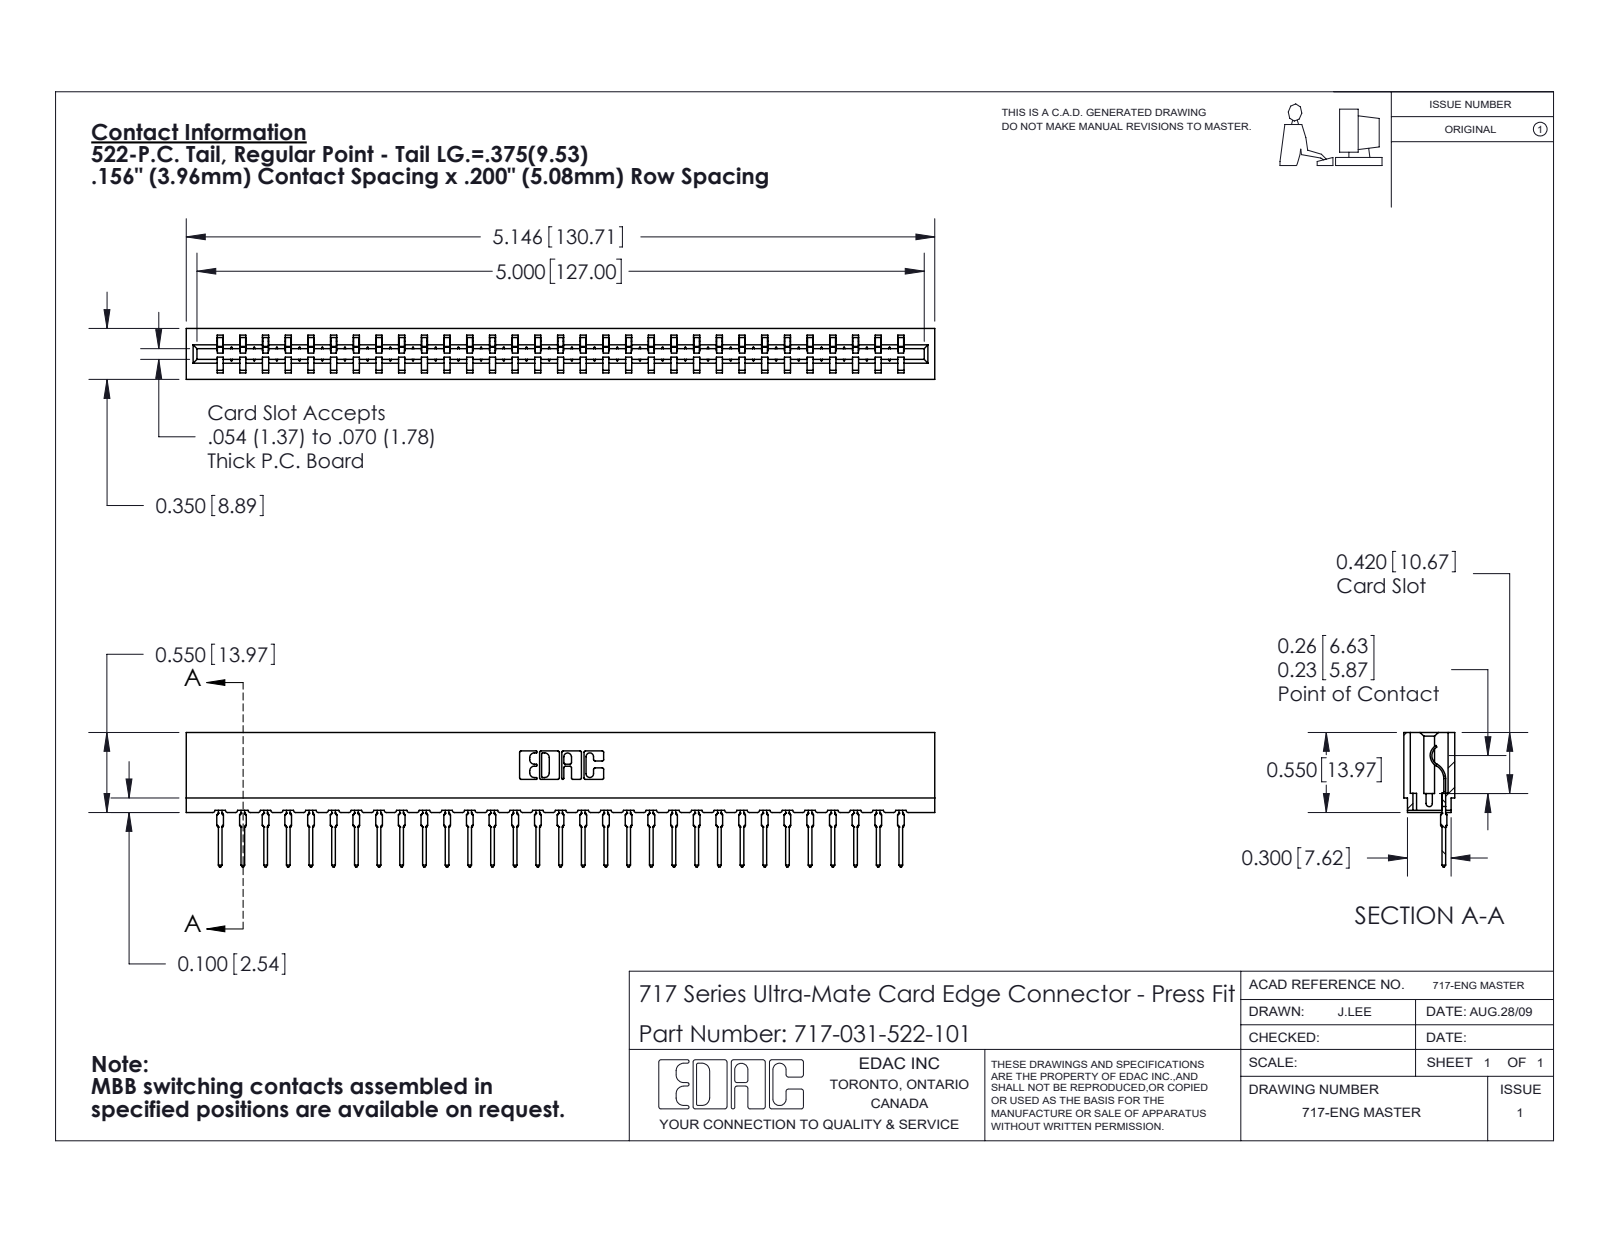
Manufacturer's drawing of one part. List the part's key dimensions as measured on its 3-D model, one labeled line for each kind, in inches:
Part name (STEP PRODUCT): 717 Part_Insulator Option - 06; 717-031-522-101; 745-292-001_522
STEP written by: SolidWorks 2020 (CONFIG_CONTROL_DESIGN)
Units: inches
Bodies: 32 solids, 3597 faces (2162 planar, 629 cylindrical, 806 other)
Overall size (bounding box): 5.146 × 0.924 × 0.35
Volume: 0.677 in³ · Surface area: 24.09 in²
Partial cylindrical surfaces — rounded edges, fillets, slot ends (radius × count): R0.015 ×62, R0.021 ×62, R0.01 ×22, R0.007 ×6, R0.031 ×6, R0.005 ×4, R0.011 ×4, R0.026 ×3
Main face-to-face distances: 0.212, 0.138, 0.35, 0.074, 0.045, 0.305, 0.093, 0.167, 0.063, 0.287
